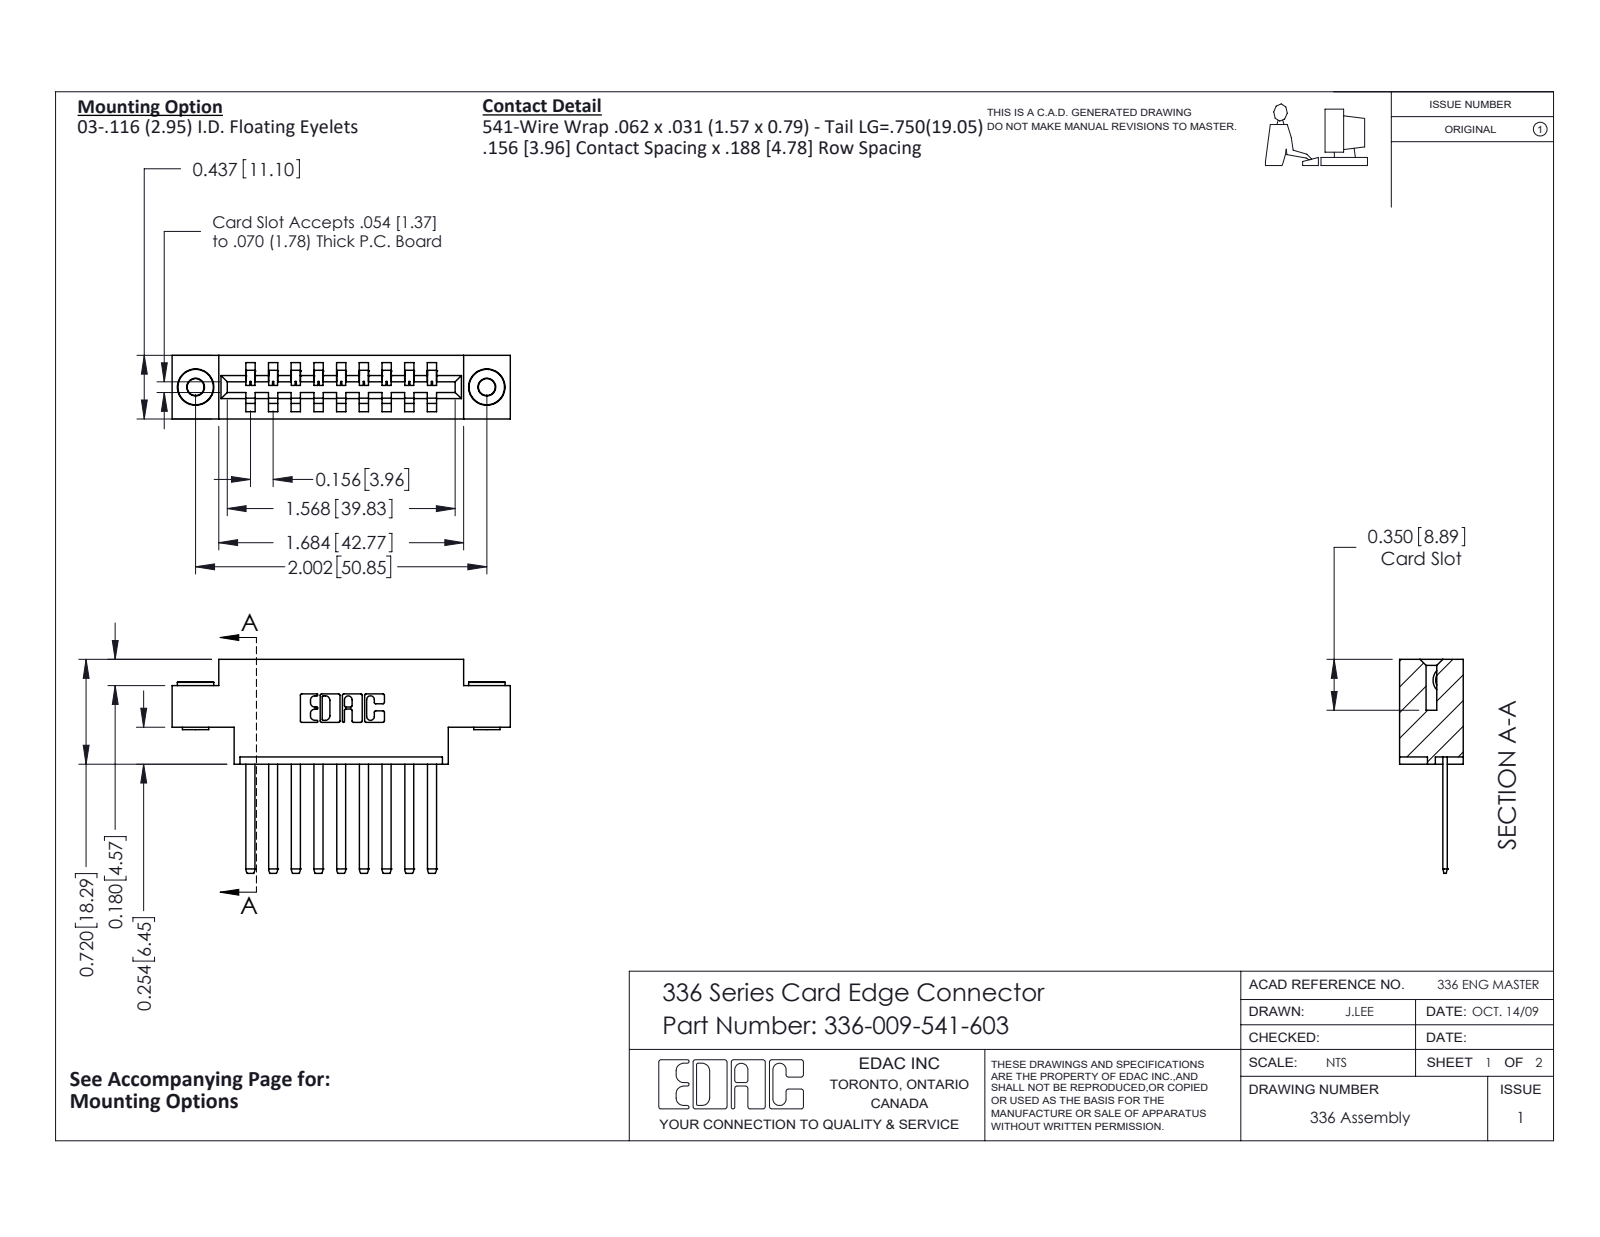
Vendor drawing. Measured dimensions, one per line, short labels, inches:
name: 336 Part_Offset - .156 Dia - TH; 336-009-541-603; 345-250-002_345-250-002-102; 336-290-001_336-290-541
written by: SolidWorks 2020 (CONFIG_CONTROL_DESIGN)
unit: in
bodies: 12 solids, 606 faces (390 planar, 208 cylindrical, 8 other)
size: 2.325 × 1.47 × 0.437
volume: 0.468 in³; area: 12.77 in²
holes: 2× ⌀0.116, 2× ⌀0.156
bosses: 2× ⌀0.25, 2× ⌀0.18, 2× ⌀0.136
rounds: 22× R0.01, 18× R0.004, 18× R0.056, 6× R0.007, 6× R0.031, 3× R0.026, 2× R0.022, 2× R0.04
face distances: 0.156, 0.437, 0.624, 0.312, 0.468, 0.78, 0.22, 0.376, 0.312, 0.404
hole spacings: 2.002
